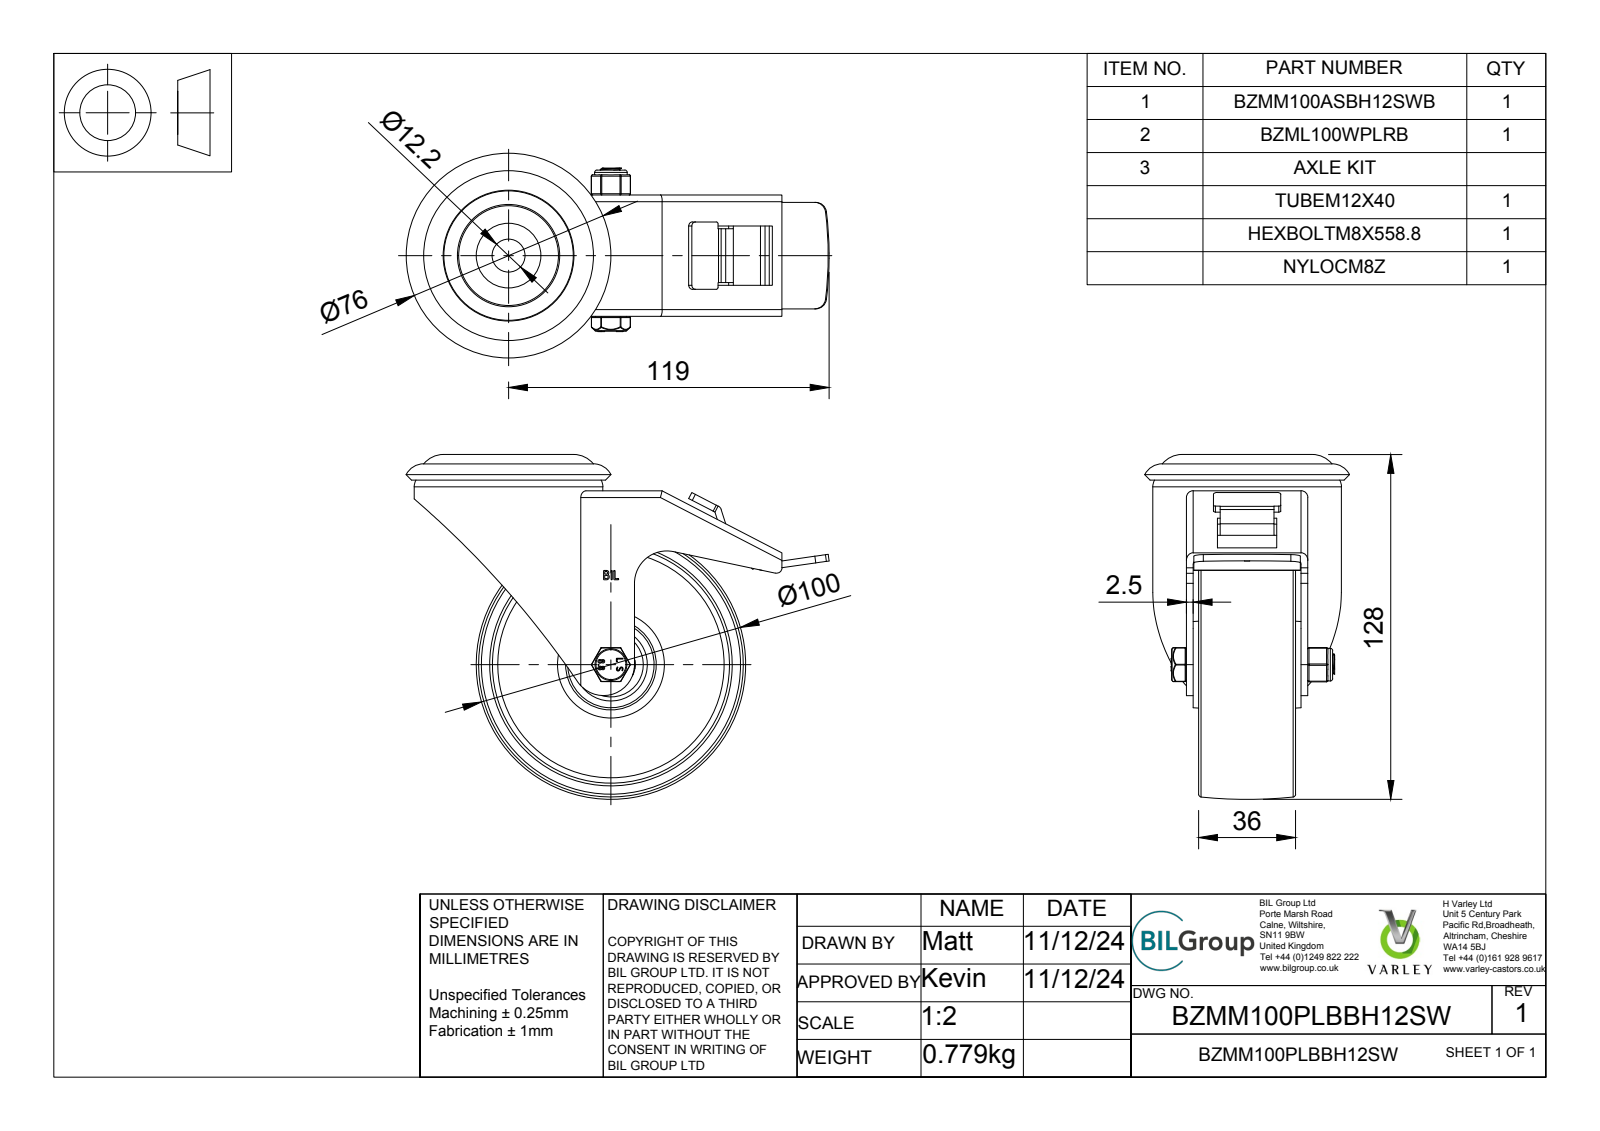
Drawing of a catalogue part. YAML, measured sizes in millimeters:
part_name: "BZMM100PLBBH12SW v3; BZMM100ASBH12SWB v1; PRESSED STEEL, ZINC PLATED HEAD; PRESSED STEEL, ZINC PLATED FORKS (+7 more)"
step_written_by: "Autodesk Translation Framework v13.20.0.188 (AP242_MANAGED_MODEL_BASED_3D_ENGINEERING_MIM_LF)"
units: millimeters
bodies: {solids: 18, faces: 664, planar: 338, cylindrical: 223, other: 103}
overall_size: [157, 128, 76]
volume: 203423
surface_area: 112703
round_holes:
  - {diameter: 0.66, count: 2}
  - {diameter: 8, count: 1}
  - {diameter: 8.2, count: 1}
  - {diameter: 8.4, count: 1}
  - {diameter: 8.6, count: 1}
  - {diameter: 12.2, count: 1}
  - {diameter: 12.5, count: 1}
  - {diameter: 18, count: 1}
  - {diameter: 27, count: 1}
  - {diameter: 65, count: 1}
  - {diameter: 72, count: 1}
  - {diameter: 88, count: 1}
round_bosses_or_shafts:
  - {diameter: 3, count: 8}
  - {diameter: 70, count: 1}
  - {diameter: 49.5, count: 1}
  - {diameter: 38, count: 1}
  - {diameter: 24, count: 1}
  - {diameter: 21.31, count: 1}
  - {diameter: 12.1, count: 1}
  - {diameter: 11.9, count: 1}
partial_cylinders:
  - {radius: 0.75, count: 50}
  - {radius: 0.5, count: 18}
  - {radius: 0.25, count: 12}
  - {radius: 1.25, count: 10}
  - {radius: 0.33, count: 4}
  - {radius: 0.64, count: 4}
  - {radius: 2.5, count: 4}
  - {radius: 2, count: 3}
face_to_face_distances: [2.5, 7, 16.5, 23.5, 19, 26, 42.5, 4.5, 2, 14.5]
hole_center_spacings: [3.22, 2.49]
